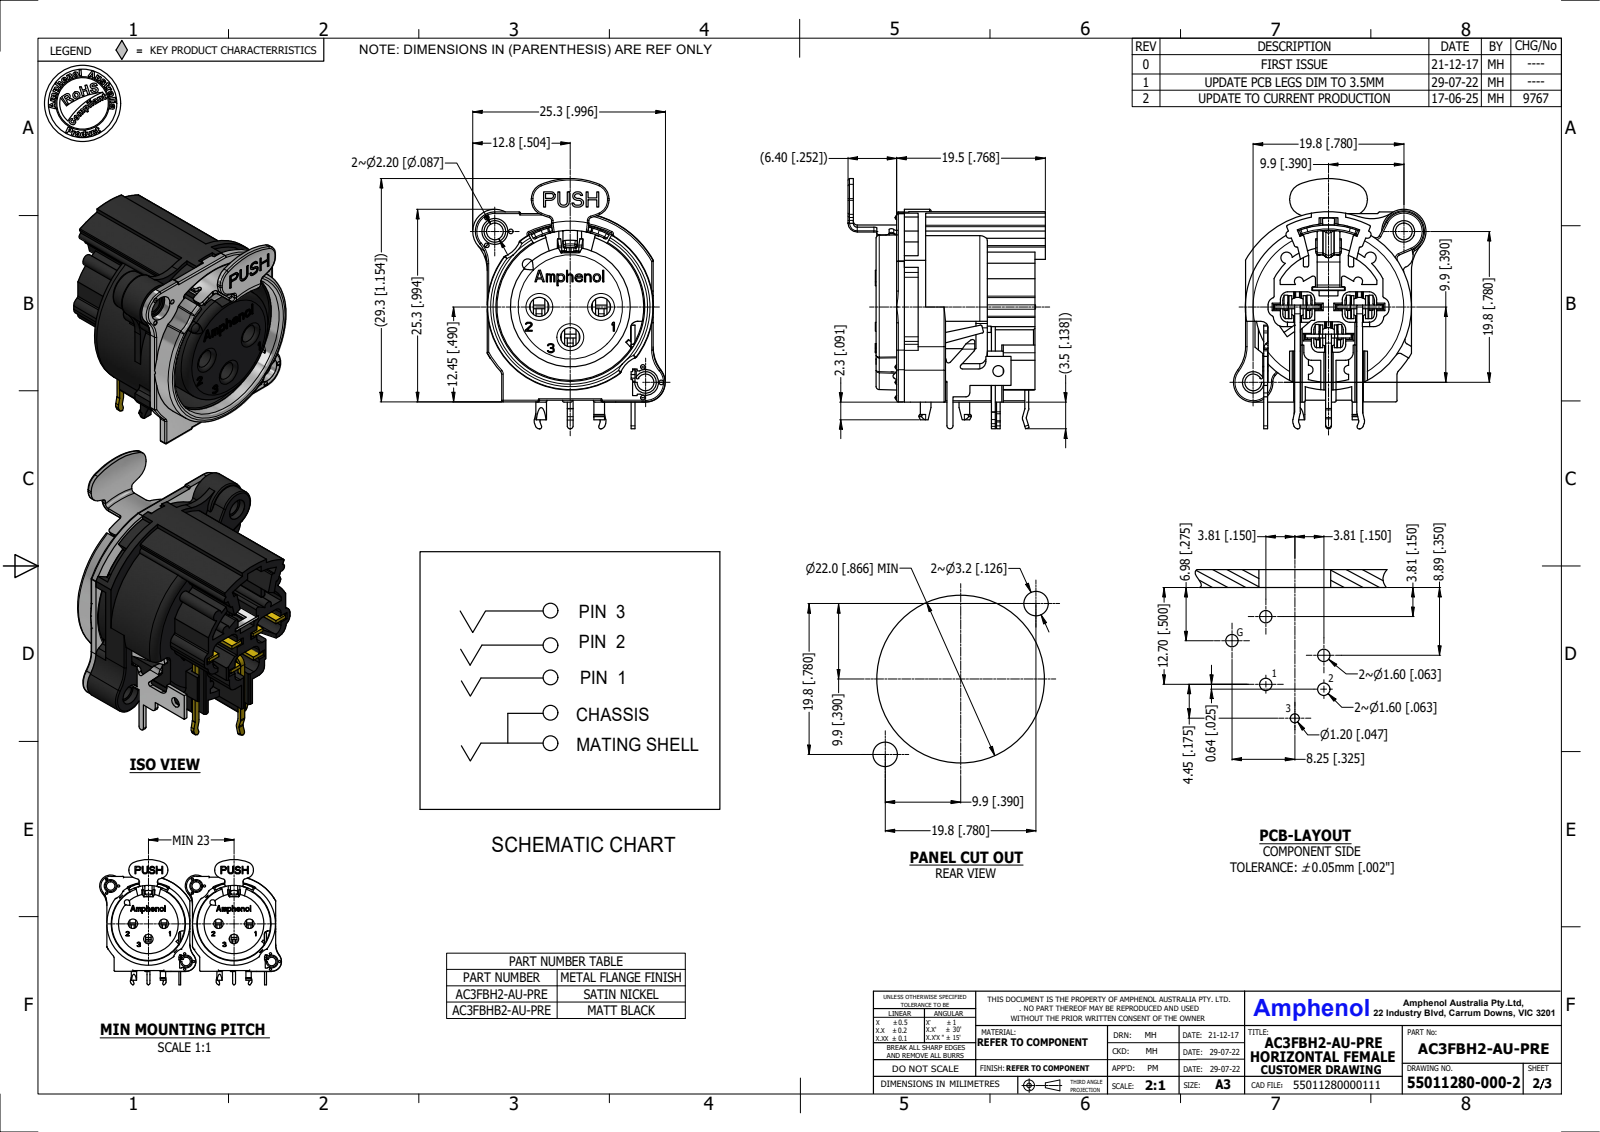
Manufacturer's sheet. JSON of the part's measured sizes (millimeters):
{"part_name": "AC3FBH2-AU-PRE simplified", "step_written_by": "Autodesk Inventor 2023 (AUTOMOTIVE_DESIGN)", "units": "millimeters", "bodies": {"solids": 1, "faces": 1237, "planar": 867, "cylindrical": 258, "other": 112}, "overall_size": [32.8, 25.9, 25.3], "volume_mm3": 7310, "surface_area_mm2": 4381, "round_holes": [[2.5, 3], [1.1, 2], [2.2, 2], [2.8, 2], [1.2, 1], [1.4, 1], [3.4, 1], [19.5, 1], [20.7, 1]], "round_bosses_or_shafts": [[1.4, 2], [1.2, 2], [20.5, 1], [19.3, 1], [15.7, 1]], "partial_cylinders_radius": [[0.2, 49], [1, 21], [0.5, 19], [0.6, 15], [0.3, 13], [0.4, 13], [0.2, 8], [2, 4]], "face_to_face_distances": [1, 17.7, 3.7, 3.2, 20.9, 11.9, 2.7, 18.2, 0.5, 6.2], "hole_center_spacings": [4.1, 5.7, 11.5, 14, 17.1, 2.9, 3.4, 4]}
